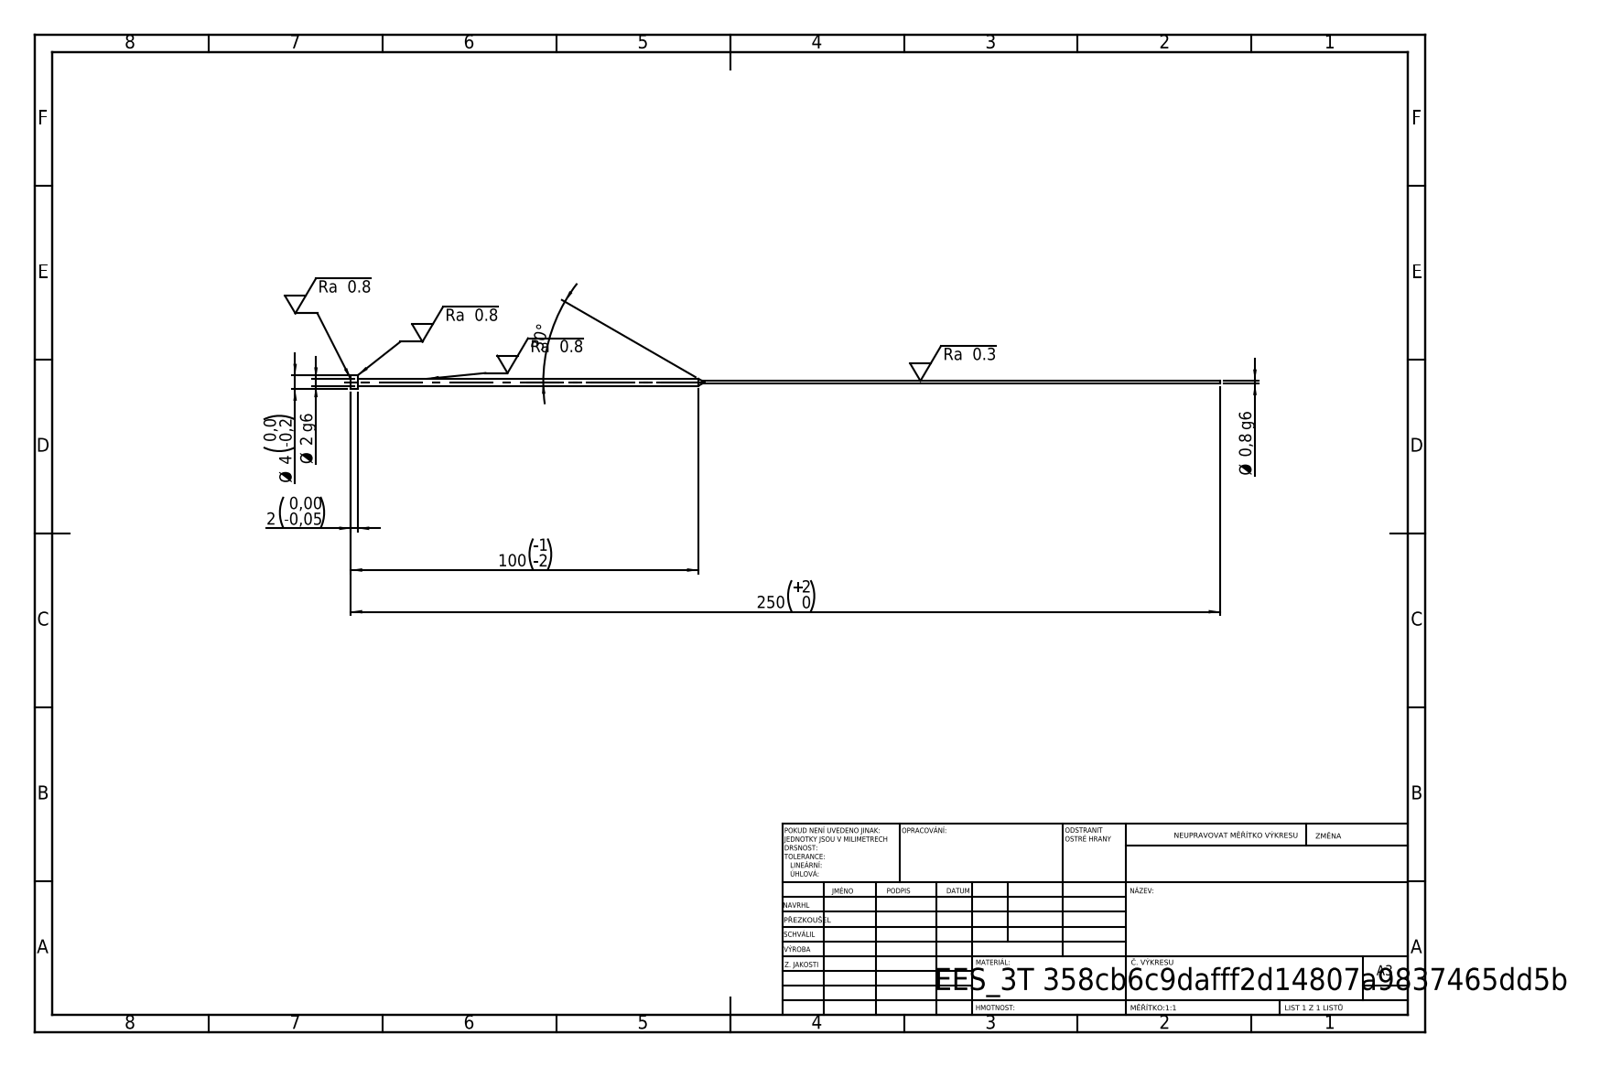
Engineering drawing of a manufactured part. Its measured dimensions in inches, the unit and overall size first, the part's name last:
Units: inches
Overall size (bounding box): 9.843 × 0.157 × 0.157
Round bosses / shafts (diameter × count): ⌀0.157 ×1, ⌀0.079 ×1, ⌀0.031 ×1
Main face-to-face distances: 0.079, 9.764, 9.843
Volume: 0.025 in³ · Surface area: 1.617 in²
Bodies: 1 solid, 11 faces (3 planar, 6 cylindrical, 2 other)
STEP written by: SolidWorks 2019 (CONFIG_CONTROL_DESIGN)
